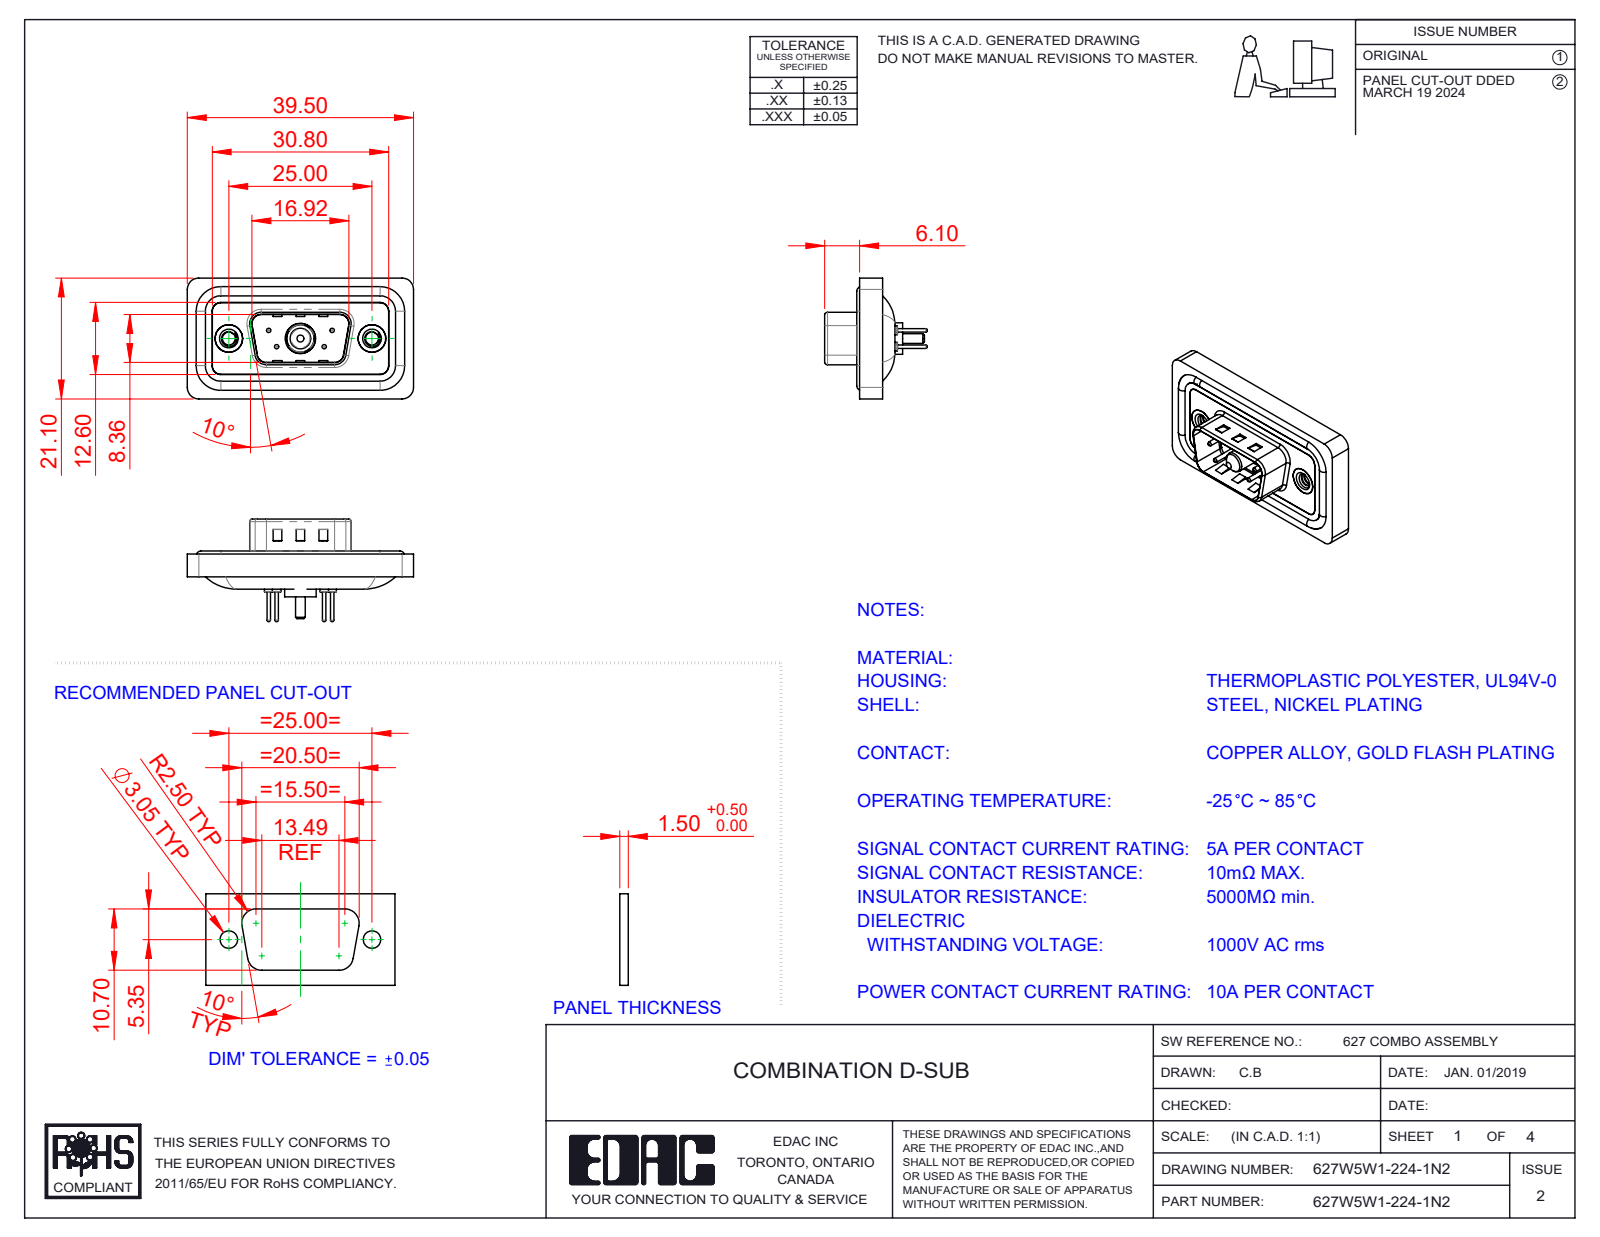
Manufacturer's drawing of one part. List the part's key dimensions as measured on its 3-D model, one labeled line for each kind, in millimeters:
Part name (STEP PRODUCT): 627W5W1-224-1N2; 627Combo Shell Rear_09 Contacts; 627Combo Shell Front_09 Contacts; Power Pin_10A S (+5 more)
STEP written by: SolidWorks 2023 (CONFIG_CONTROL_DESIGN)
Units: millimetres
Bodies: 13 solids, 598 faces (183 planar, 255 cylindrical, 160 other)
Overall size (bounding box): 39.5 × 21.1 × 17.9
Volume: 4 373 mm³ · Surface area: 6 929 mm²
Round holes (diameter × count): ⌀0.75 ×4, ⌀1.6 ×4, ⌀2 ×4, ⌀2.26 ×2, ⌀4 ×2, ⌀4.8 ×2, ⌀5 ×2, ⌀4.85 ×1, ⌀5.3 ×1
Round bosses / shafts (diameter × count): ⌀1.6 ×4, ⌀1.5 ×4, ⌀0.6 ×4, ⌀4.9 ×2, ⌀5.5 ×1, ⌀5.2 ×1, ⌀4.75 ×1, ⌀3.75 ×1
Partial cylindrical surfaces — rounded edges, fillets, slot ends (radius × count): R1.5 ×22, R2 ×18, R0.5 ×8, R1.6 ×8, R0.25 ×4, R0.6 ×4, R0.65 ×4, R0.9 ×4
Main face-to-face distances: 0.4, 1.1, 2.9, 1.6, 1.5, 3.1, 0.5, 2.5, 4, 0.8
Hole centre spacings: 3.16, 5.72, 7.1, 12.5, 18.1, 4.39, 4.4, 8.31
